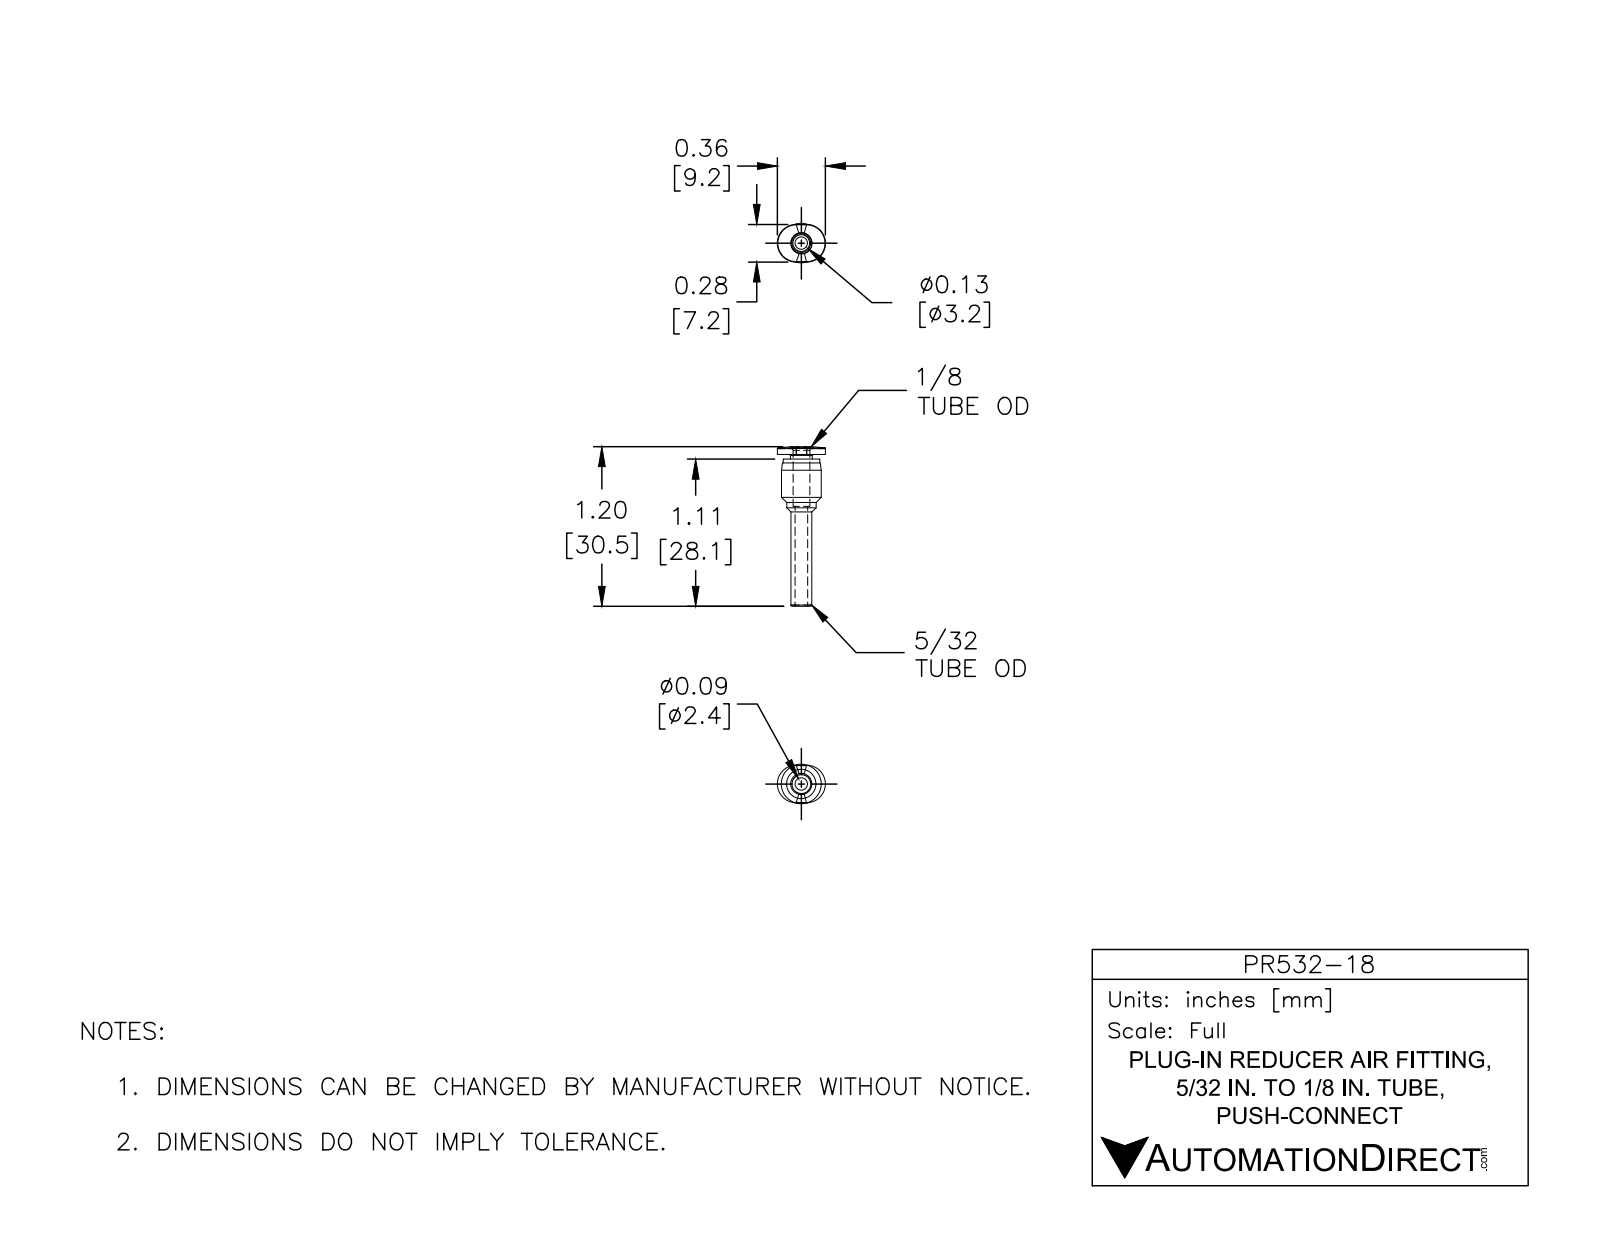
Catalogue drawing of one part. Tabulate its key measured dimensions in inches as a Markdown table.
| quantity | value |
| --- | --- |
| part name | PR532-18 |
| STEP written by | SolidWorks 2015 (CONFIG_CONTROL_DESIGN) |
| units | inches |
| bodies | 1 solid, 50 faces (8 planar, 16 cylindrical, 26 other) |
| overall size | 1.201 × 0.362 × 0.299 |
| volume | 0.032 in³ |
| surface area | 1.375 in² |
| round holes (diameter × count) | 0.094 × 1, 0.126 × 1 |
| round bosses / shafts (diameter × count) | 0.299 × 1, 0.276 × 1, 0.22 × 1, 0.165 × 1, 0.157 × 1 |
| partial cylindrical surfaces (radius × count) | 0.142 × 2 |
| main face-to-face distances | 0.035, 1.106, 1.142, 0.752, 0.354, 0.39, 0.283, 1.079, 0.327, 0.028 |
